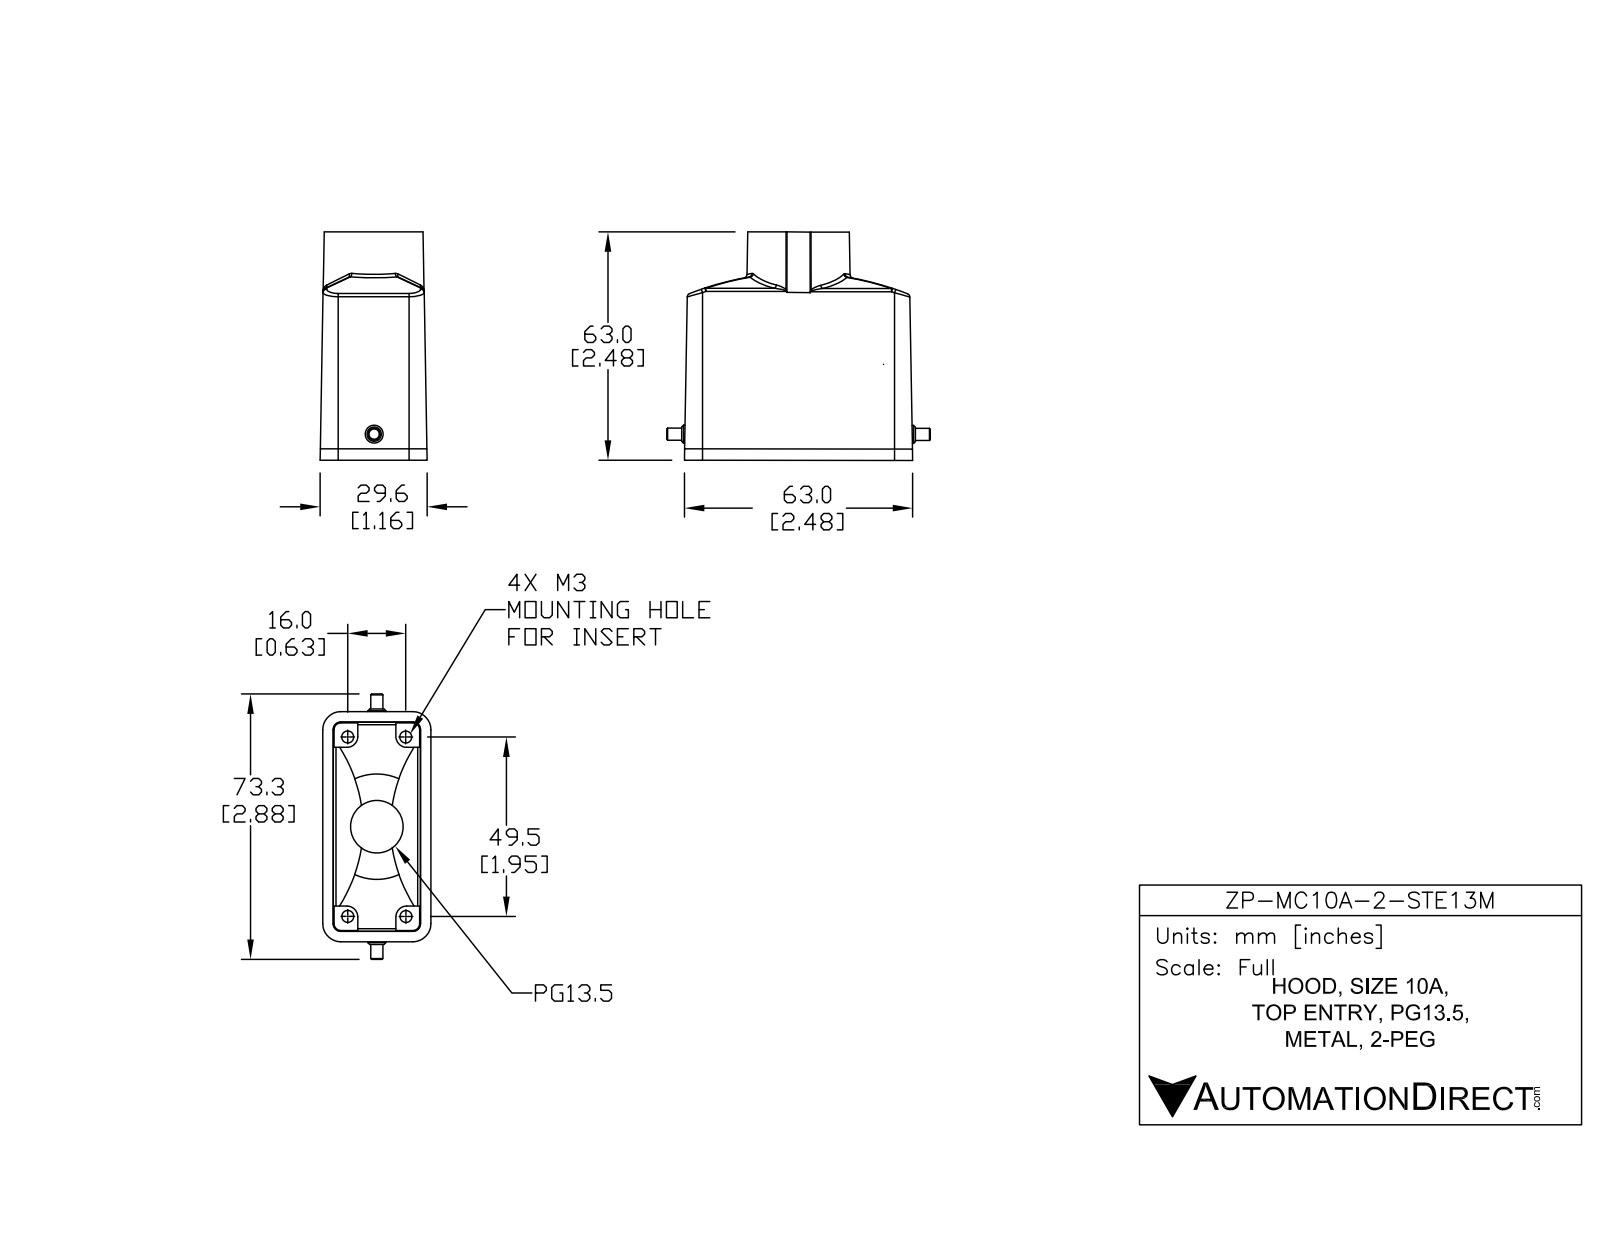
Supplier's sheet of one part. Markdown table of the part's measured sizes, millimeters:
| quantity | value |
| --- | --- |
| part name | ZP-MC10A-2-STE13M |
| STEP written by | SolidWorks 2014 (AUTOMOTIVE_DESIGN) |
| units | millimeters |
| bodies | 1 solid, 220 faces (58 planar, 89 cylindrical, 73 other) |
| overall size | 73.25 × 63.32 × 29.85 |
| volume | 34 604 mm³ |
| surface area | 22 183 mm² |
| round holes (diameter × count) | 3 × 4, 14.5 × 1, 19.2 × 1 |
| round bosses / shafts (diameter × count) | 4.95 × 1, 3.35 × 1 |
| partial cylindrical surfaces (radius × count) | 1 × 4, 3 × 4, 25.65 × 2, 111.46 × 2, 124.56 × 2, 154.25 × 2, 155.71 × 2, 159.01 × 2 |
| main face-to-face distances | 2.85, 2.86, 2.63, 2.62, 63.32, 10, 2.83, 43.5, 14.6, 48.72 |
| hole center spacings | 26.01, 16, 49.5, 52.02 |
